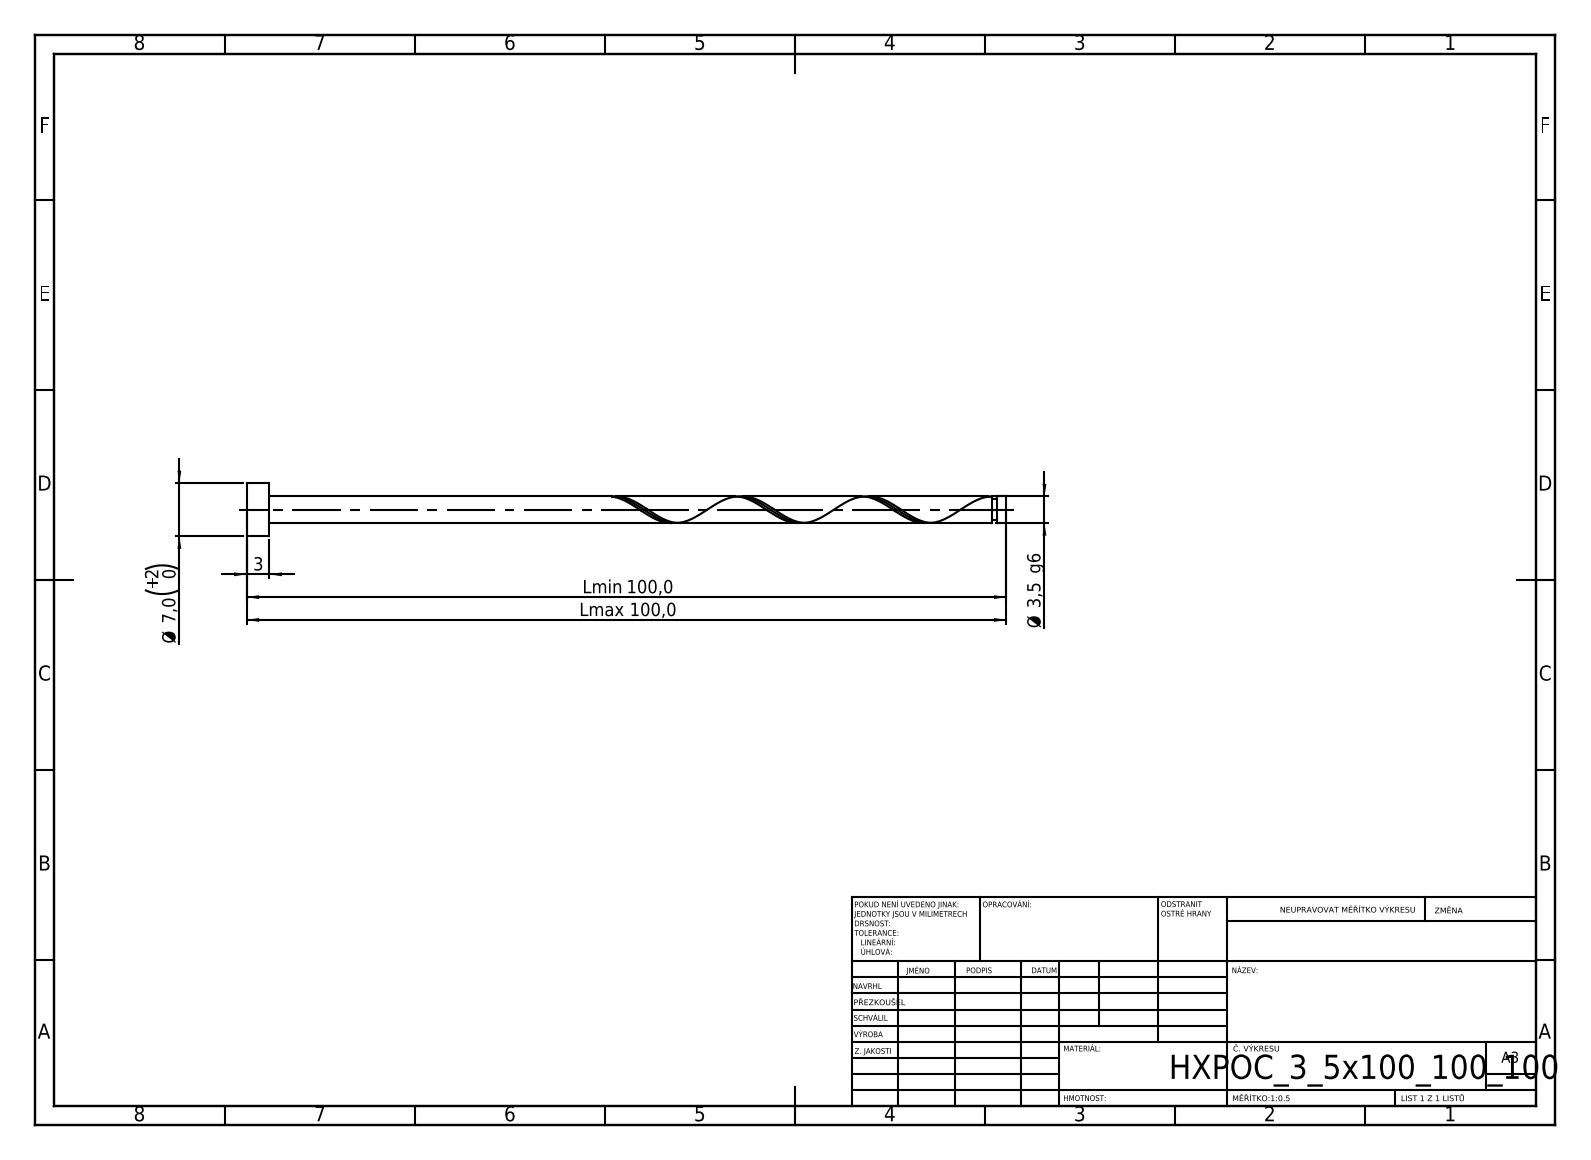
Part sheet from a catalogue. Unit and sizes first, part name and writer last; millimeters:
Units: millimetres
Overall size (bounding box): 100 × 7 × 7
Round bosses / shafts (diameter × count): ⌀7 ×1, ⌀3.5 ×1, ⌀2.8 ×1
Main face-to-face distances: 3, 100, 97, 98.81, 95.81, 1.19, 98.11, 95.11, 0.7, 1.89
Volume: 1 037 mm³ · Surface area: 1 236 mm²
Bodies: 1 solid, 21 faces (6 planar, 14 cylindrical, 1 other)
STEP written by: SolidWorks 2019 (CONFIG_CONTROL_DESIGN)
